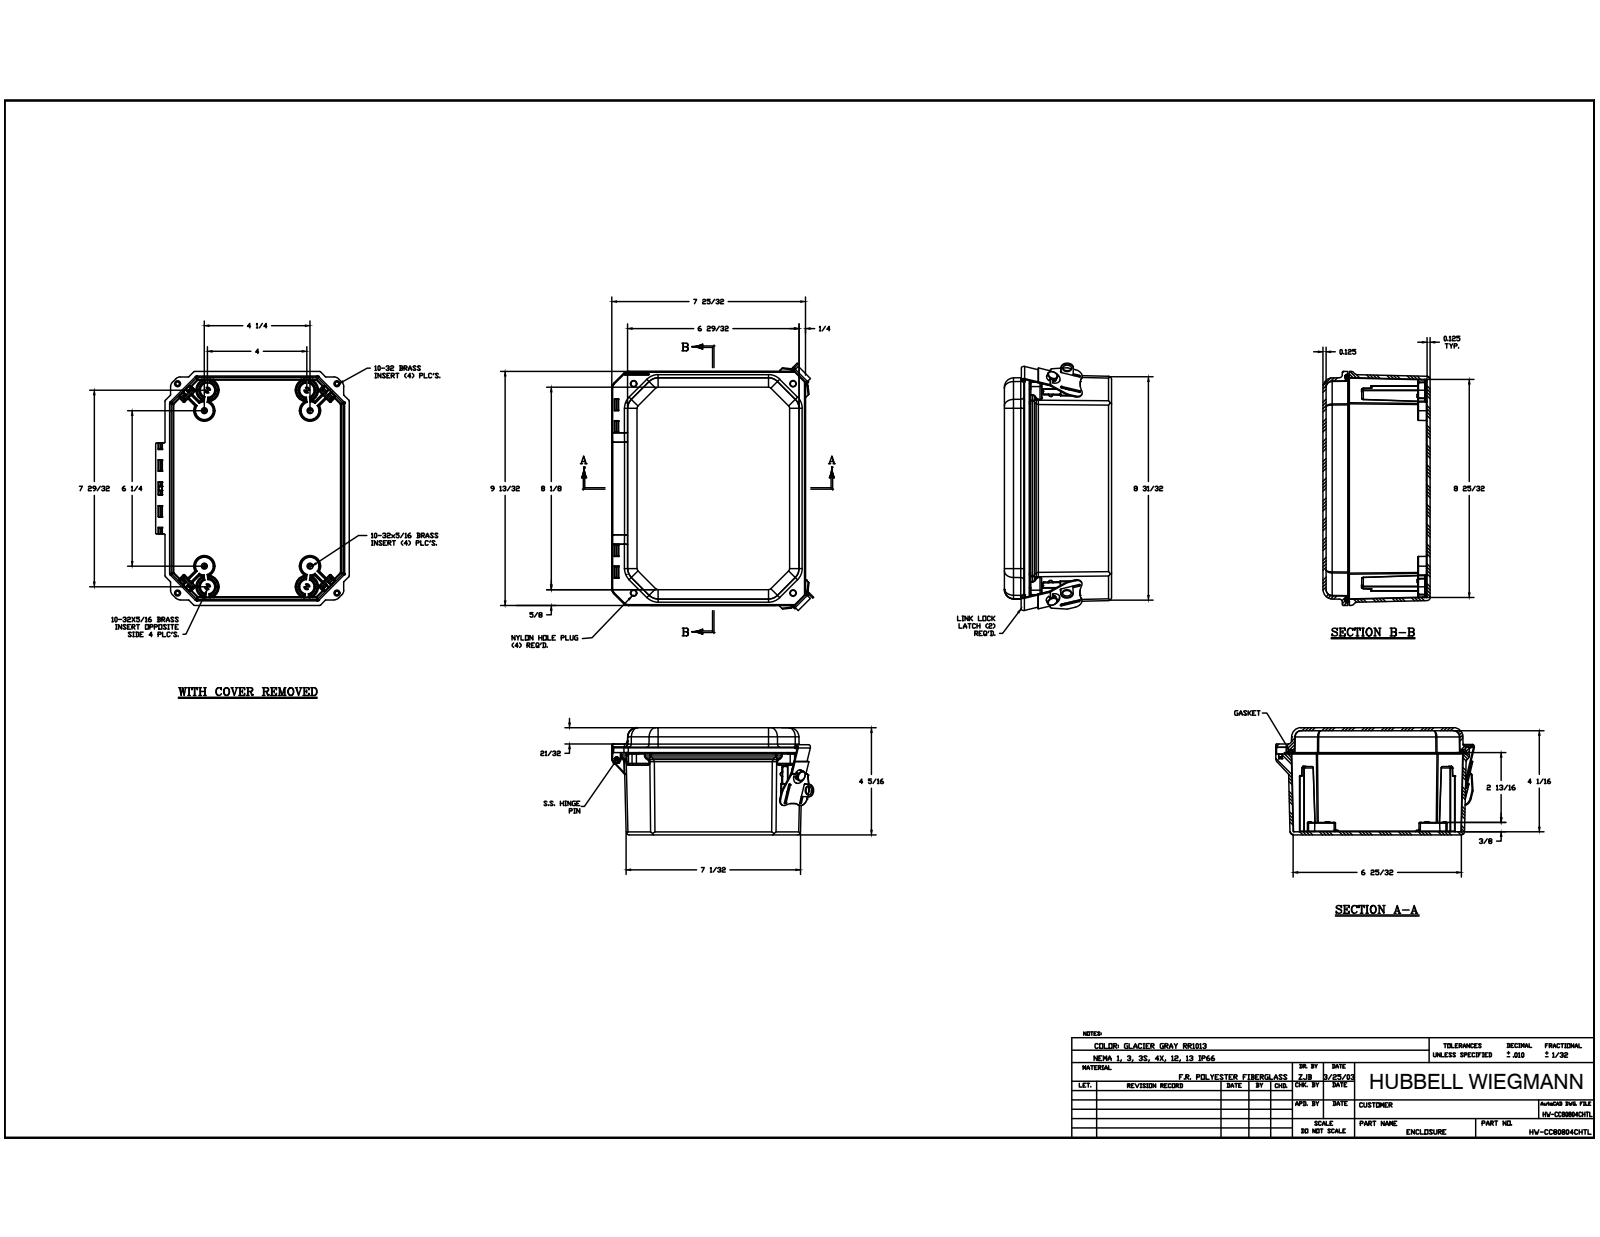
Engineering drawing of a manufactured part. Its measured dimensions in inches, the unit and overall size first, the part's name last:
Units: inches
Overall size (bounding box): 10.263 × 8.214 × 4.312
Round holes (diameter × count): ⌀0.156 ×12, ⌀0.152 ×8, ⌀0.098 ×4, ⌀0.15 ×4, ⌀0.219 ×4, ⌀0.252 ×4, ⌀0.312 ×4, ⌀0.05 ×2, ⌀0.12 ×2, ⌀0.363 ×2, ⌀0.137 ×1
Round bosses / shafts (diameter × count): ⌀0.246 ×12, ⌀0.87 ×4, ⌀0.209 ×4, ⌀0.2 ×4, ⌀0.135 ×3, ⌀0.6 ×2, ⌀0.05 ×2
Partial cylindrical surfaces — rounded edges, fillets, slot ends (radius × count): R0.01 ×155, R0.005 ×94, R0.02 ×67, R0.125 ×41, R0.03 ×36, R0.039 ×28, R0.25 ×26, R0.03 ×24
Main face-to-face distances: 0.125, 4.187, 4.312, 4.062, 0.124, 3.531, 0.656, 0.875, 1, 3.312
Hole centre spacings: 7.411, 8.193, 9.065, 0.837, 1.53, 4.207, 5.439, 7.08
Volume: 38.92 in³ · Surface area: 609.5 in²
Bodies: 31 solids, 2229 faces (656 planar, 853 cylindrical, 720 other)
Part name (STEP PRODUCT): DS080604BOX; DSCC080604CVR; GA806; WP806HLU (+6 more)
STEP written by: Autodesk Inventor 2014 (AUTOMOTIVE_DESIGN)
